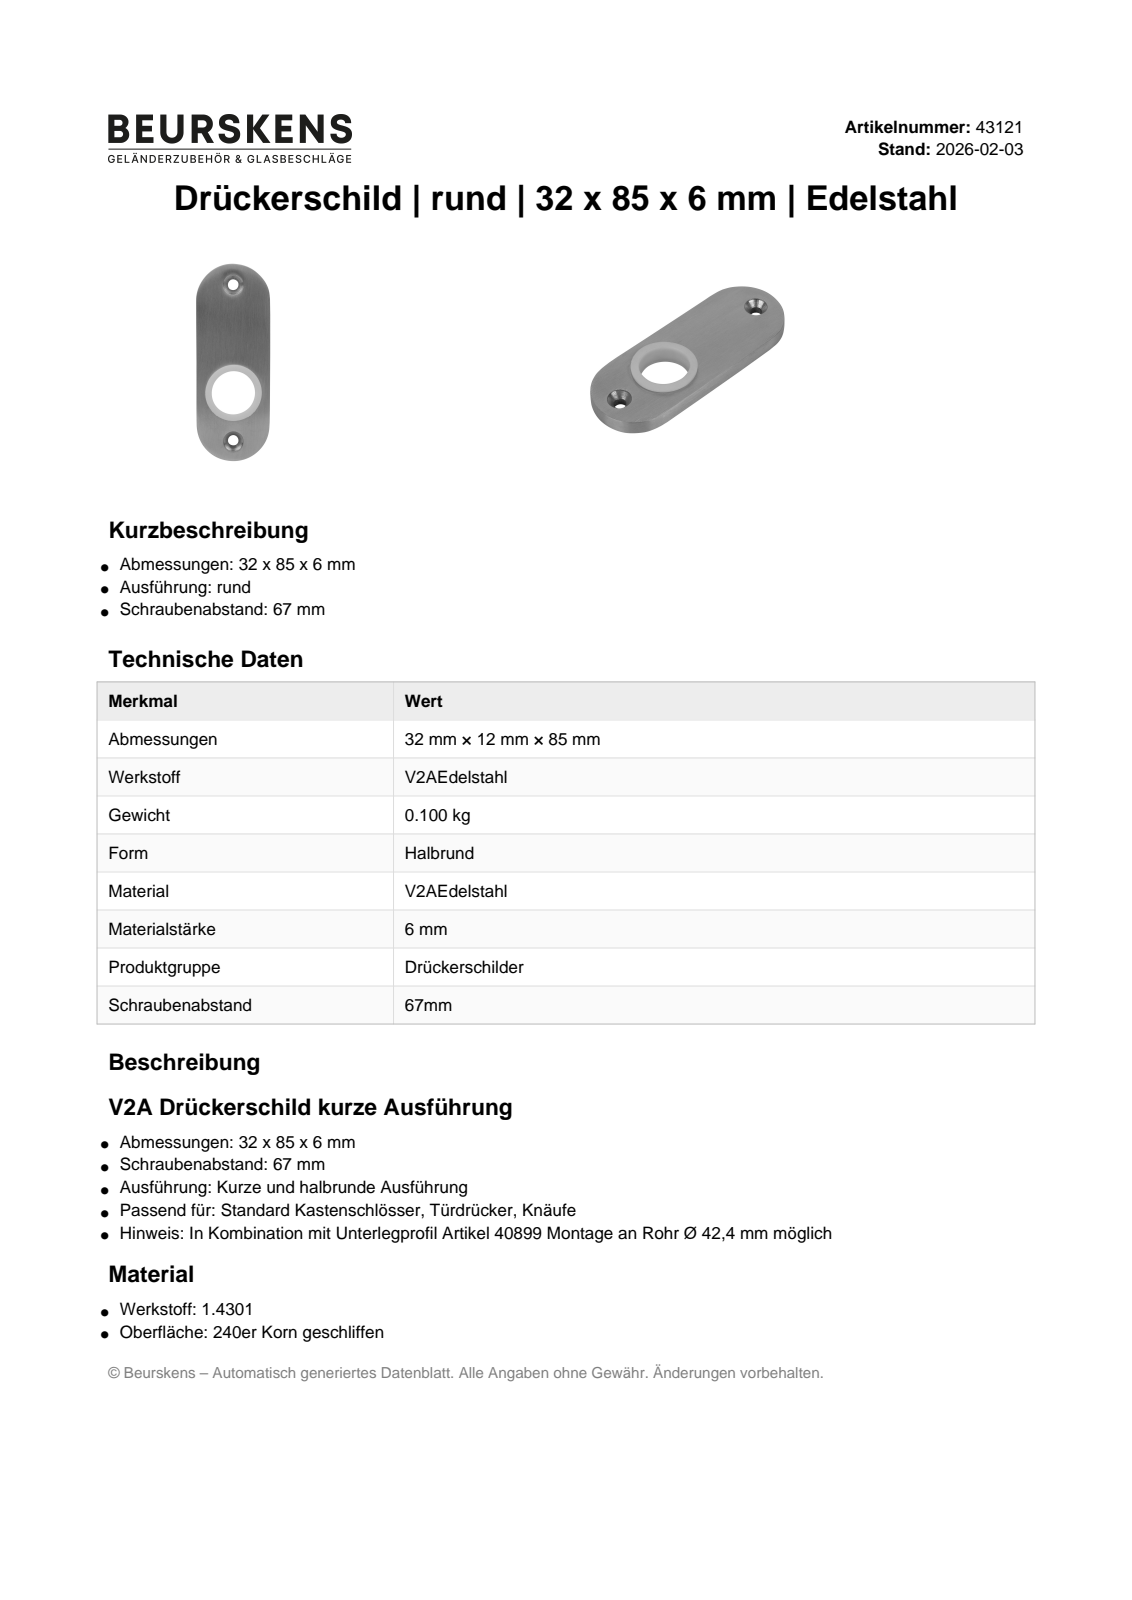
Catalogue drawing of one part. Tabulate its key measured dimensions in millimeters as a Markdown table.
| quantity | value |
| --- | --- |
| part name | 43121 |
| STEP written by | Autodesk Inventor 2022 (AUTOMOTIVE_DESIGN) |
| units | millimeters |
| bodies | 1 solid, 13 faces (5 planar, 6 cylindrical, 2 other) |
| overall size | 85 × 32 × 7 |
| volume | 12 844 mm³ |
| surface area | 6 174 mm² |
| round holes (diameter × count) | 4.5 × 2, 21 × 1 |
| round bosses / shafts (diameter × count) | 26 × 1 |
| partial cylindrical surfaces (radius × count) | 16 × 2 |
| main face-to-face distances | 6, 32, 7, 1 |
| hole center spacings | 21, 46, 67 |
